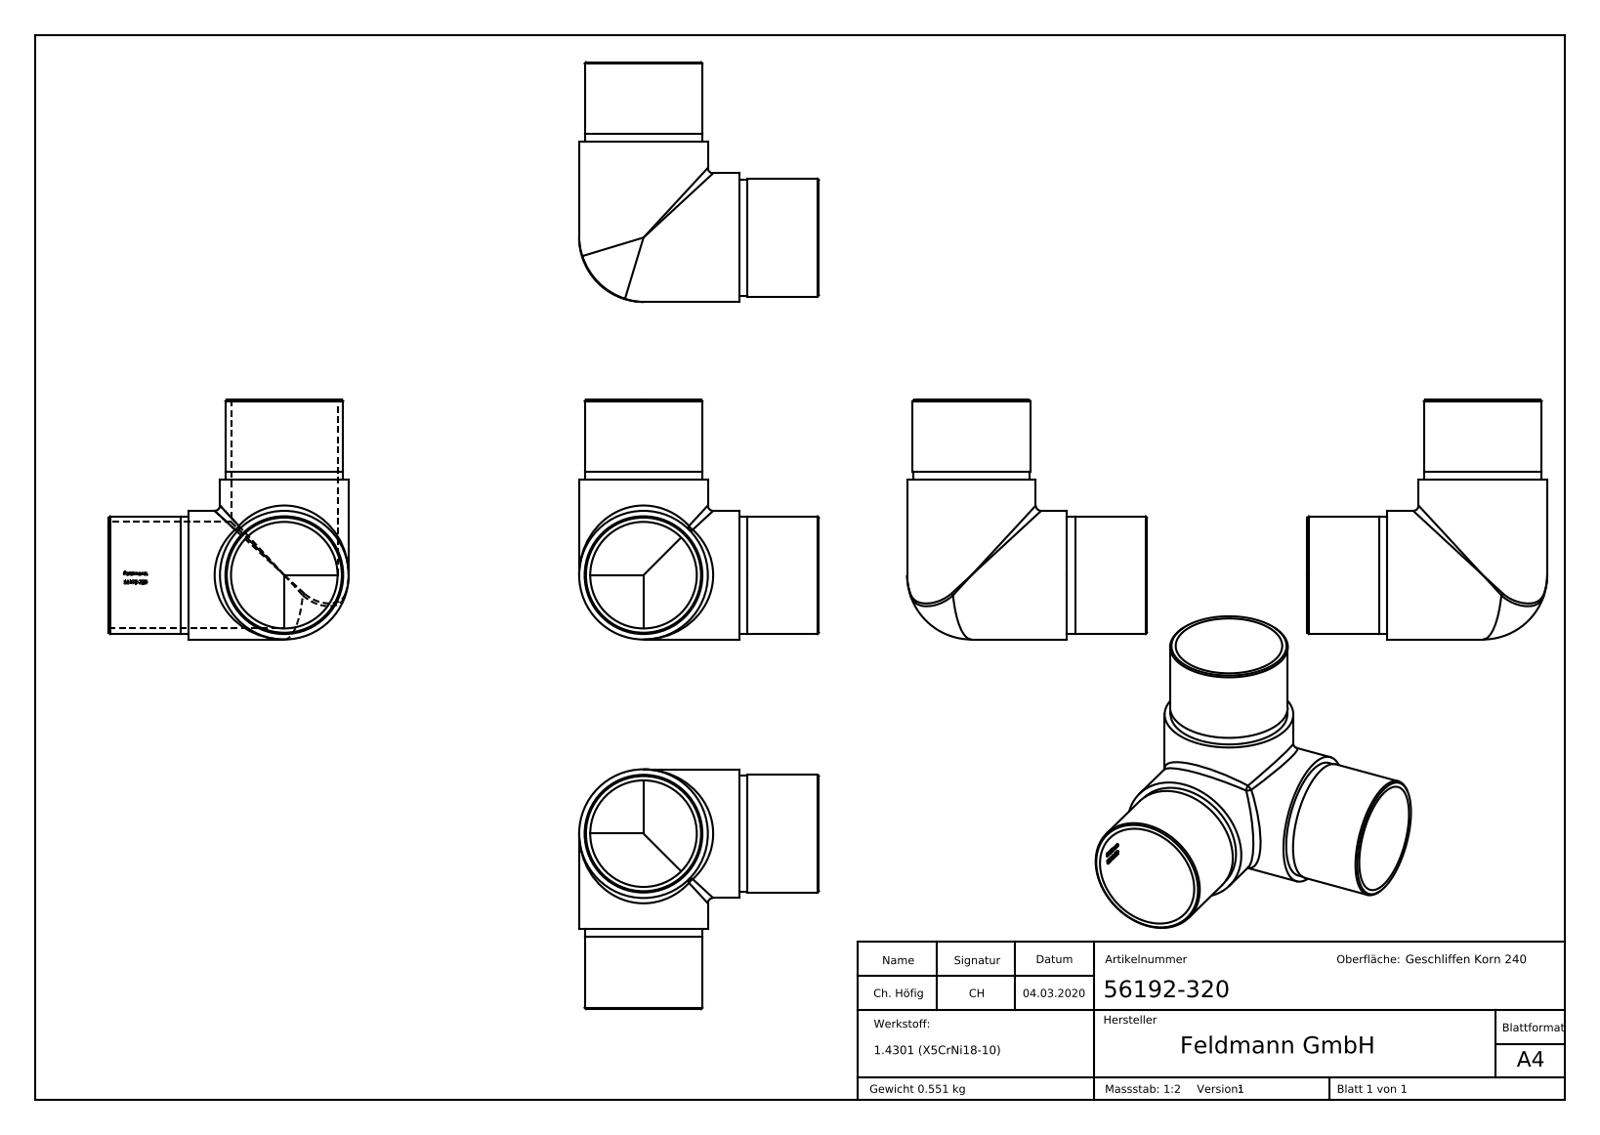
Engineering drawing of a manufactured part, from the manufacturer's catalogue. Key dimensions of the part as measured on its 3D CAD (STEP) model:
Part name (STEP PRODUCT): 56192-320
STEP written by: SolidWorks 2015 (CONFIG_CONTROL_DESIGN)
Units: millimetres
Bodies: 1 solid, 254 faces (94 planar, 36 cylindrical, 124 other)
Overall size (bounding box): 90 × 90 × 90
Volume: 69 717 mm³ · Surface area: 46 876 mm²
Round holes (diameter × count): ⌀40 ×3
Round bosses / shafts (diameter × count): ⌀48.3 ×3, ⌀44.2 ×3, ⌀43.8 ×3
Partial cylindrical surfaces — rounded edges, fillets, slot ends (radius × count): R20.1 ×1
Main face-to-face distances: 30, 3, 27, 0.39, 1.26, 2.97, 1.65, 3.27, 4.23, 1.32
